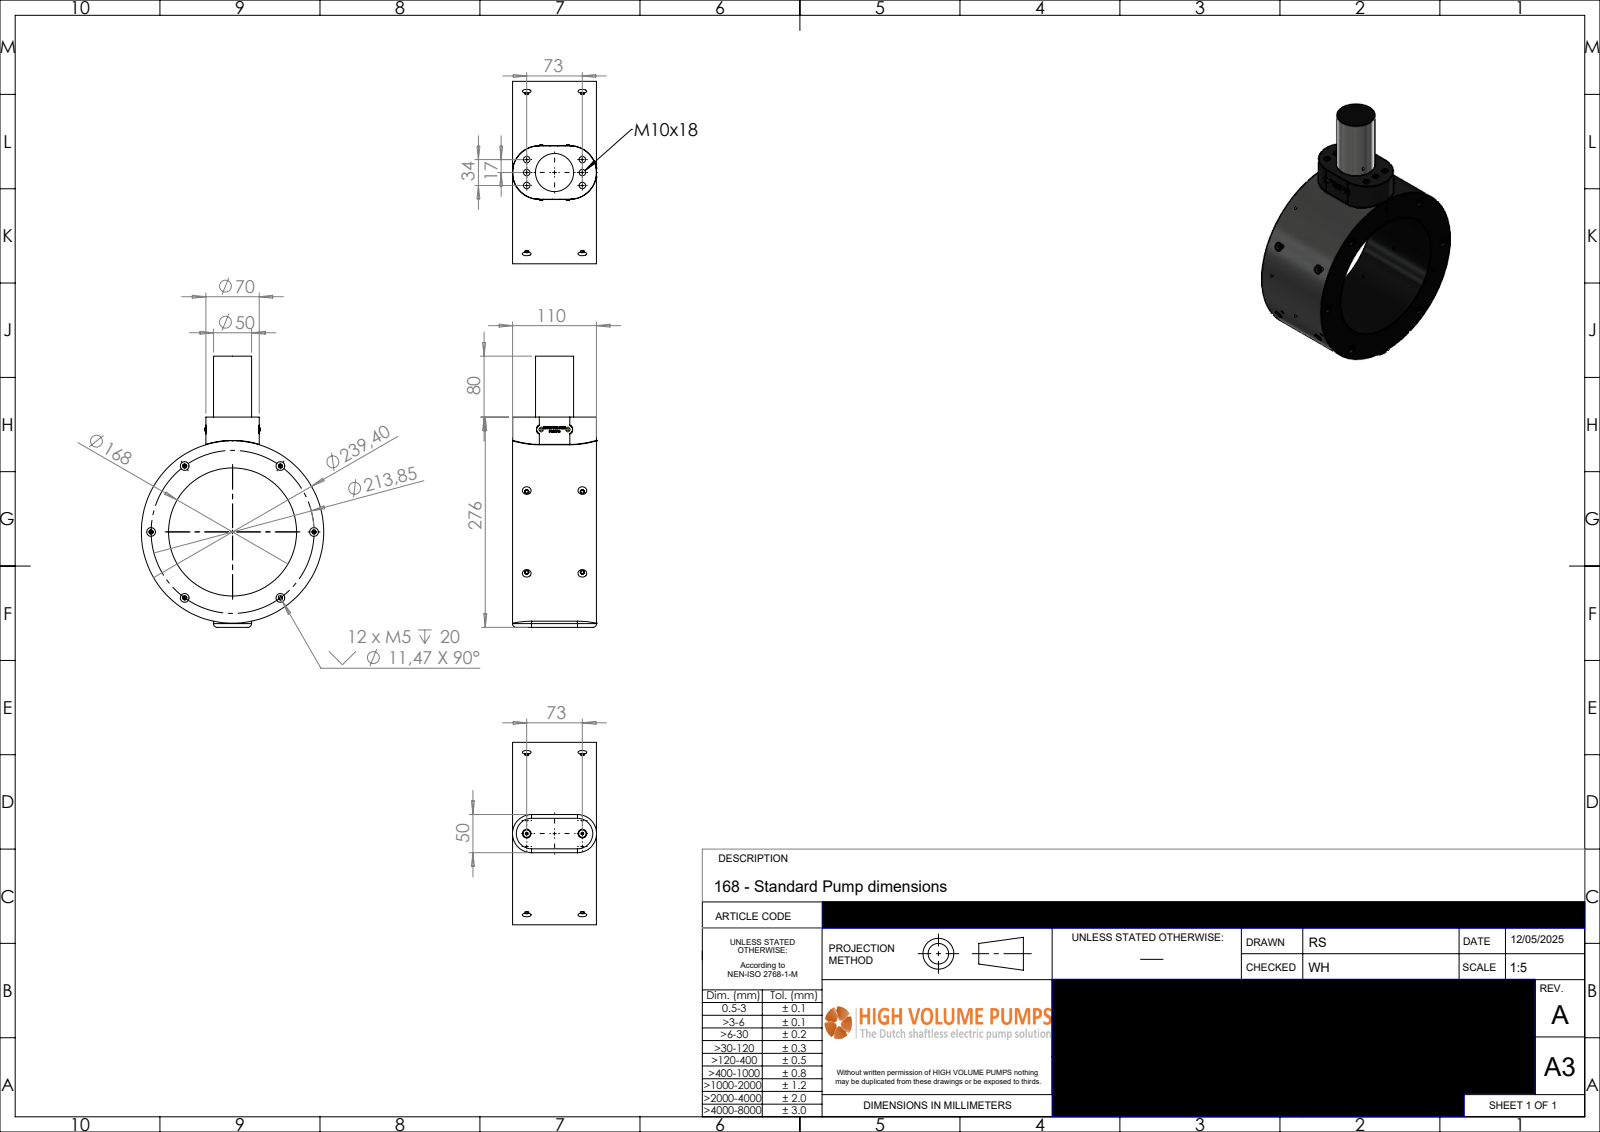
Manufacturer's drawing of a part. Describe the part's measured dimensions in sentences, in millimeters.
The part is named "P-168-030-rev-A-SP". Its 3-D file was written by "SolidWorks 2024 (AUTOMOTIVE_DESIGN)". It is 1 solid with 748 faces: 367 planar, 177 cylindrical and 204 other. Overall it measures 355.85 by 239.4 by 110.36 millimeters. Its volume is 2 902 000 cubic millimeters and its surface area 219 222 square millimeters. Round holes: 12 of diameter 4.2, 6 of diameter 5.5, 6 of diameter 8.5, 2 of diameter 3.5, 1 of diameter 168. Round bosses or shafts: 6 of diameter 5.5, 2 of diameter 9.64, 2 of diameter 5.7, 2 of diameter 3, 1 of diameter 239.4, 1 of diameter 50. Partial cylindrical surfaces (rounded edges, fillets, slot ends): 2 of radius 0.5, 2 of radius 5, 2 of radius 6.15, 2 of radius 6.25, 2 of radius 25, 2 of radius 34.5, 2 of radius 35. The main face-to-face distances are 110.06, 275.84, 355.84, 80, 70, 10, 60, 255.4, 20.44, 100.44. The hole center spacings are 73, 17, 74.95, 106.92, 190.54, 213.85, 34, 80.53.
